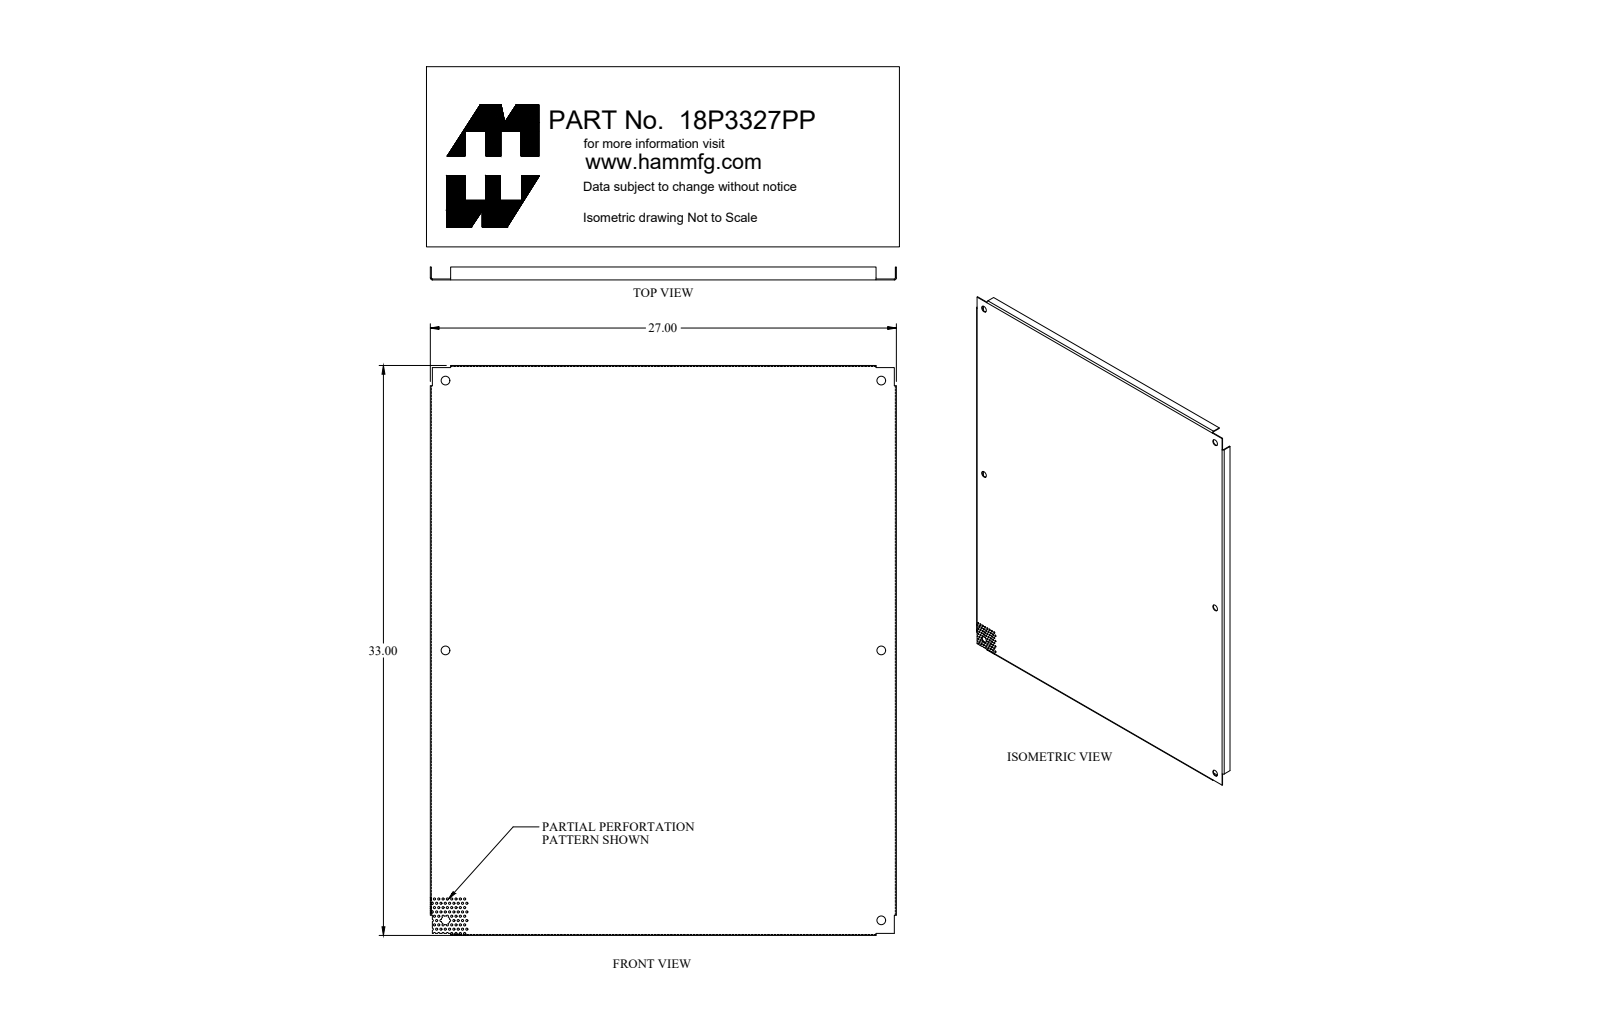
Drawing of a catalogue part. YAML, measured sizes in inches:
part_name: "18P3327PP_Default"
step_written_by: "SolidWorks 2018 (CONFIG_CONTROL_DESIGN)"
units: inches
bodies: {solids: 1, faces: 258, planar: 43, cylindrical: 207, other: 8}
overall_size: [33, 27, 0.75]
volume: 54.82
surface_area: 1933
round_holes:
  - {diameter: 0.125, count: 74}
  - {diameter: 0.5, count: 5}
partial_cylinders:
  - {radius: 0.063, count: 17}
  - {radius: 0.062, count: 8}
  - {radius: 0.029, count: 4}
  - {radius: 0.086, count: 4}
  - {radius: 0.25, count: 1}
face_to_face_distances: [0.057, 26.943, 32.943, 26.886, 27, 32.886, 33, 0.75, 0.693, 0.102]
hole_center_spacings: [0.28, 0.5, 0.25, 0.559, 0.451, 0.673, 0.707, 0.75]
